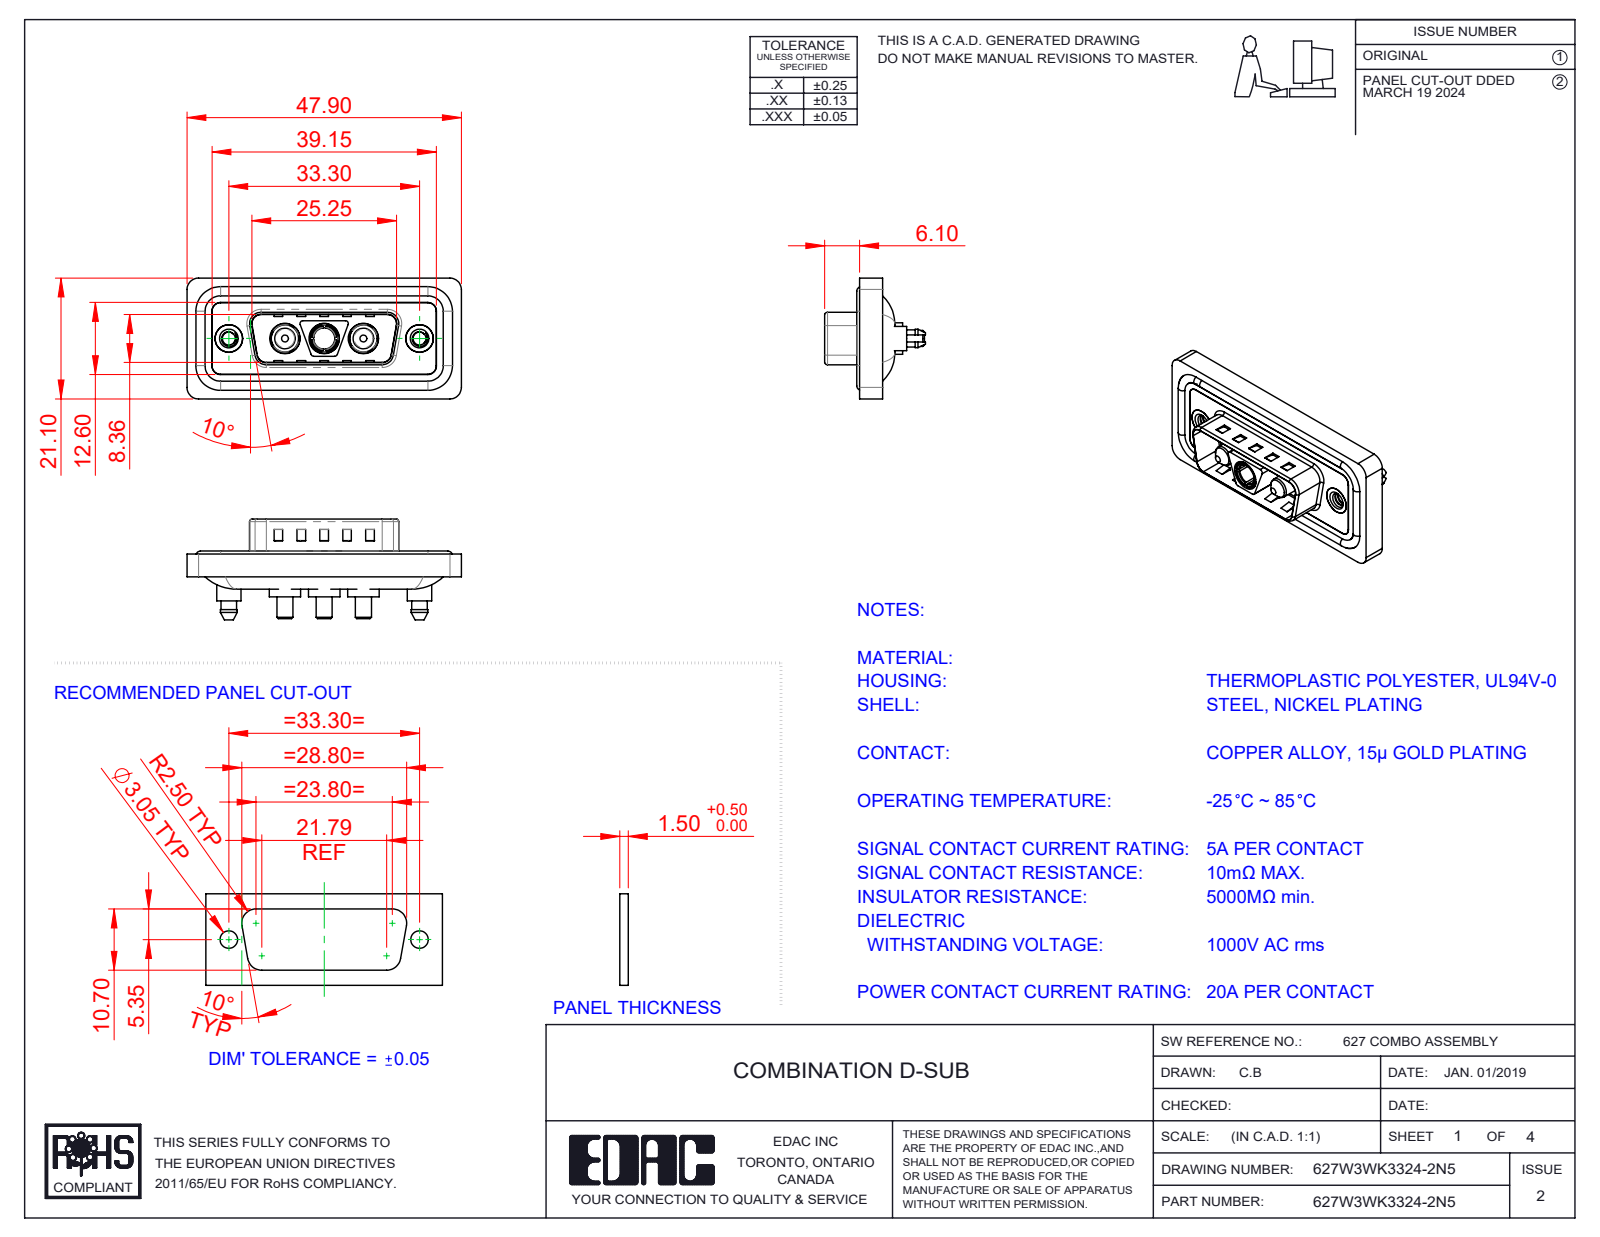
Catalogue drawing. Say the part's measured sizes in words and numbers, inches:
The part is named "Power Socket_20A S; 627Combo Shell Front_15 Contacts; 627Combo Shell Rear_15 Contacts; 627Combo Waterproof Housing_15 Contacts (+4 more)". Its 3-D file was written by "SolidWorks 2023 (CONFIG_CONTROL_DESIGN)". It is 13 solids with 659 faces: 247 planar, 282 cylindrical and 130 other. Overall it measures 1.886 by 0.831 by 0.693 inches. Its volume is 0.355 cubic inches and its surface area 14.66 square inches. Round holes: 3 of diameter 0.191, 3 of diameter 0.209, 2 of diameter 0.089, 2 of diameter 0.157, 2 of diameter 0.189, 2 of diameter 0.197, 1 of diameter 0.146. Round bosses or shafts: 4 of diameter 0.063, 3 of diameter 0.217, 3 of diameter 0.205, 3 of diameter 0.187, 3 of diameter 0.148, 3 of diameter 0.11, 2 of diameter 0.213, 2 of diameter 0.193. Partial cylindrical surfaces (rounded edges, fillets, slot ends): 28 of radius 0.059, 20 of radius 0.079, 12 of radius 0.02, 10 of radius 0.063, 4 of radius 0.01, 4 of radius 0.024, 4 of radius 0.026, 4 of radius 0.035. The main face-to-face distances are 0.016, 0.043, 0.059, 0.02, 0.063, 0.122, 0.114, 0.157, 0.028, 0.032. The hole center spacings are 0.27, 0.386, 0.656, 0.925, 0.539, 1.311.
